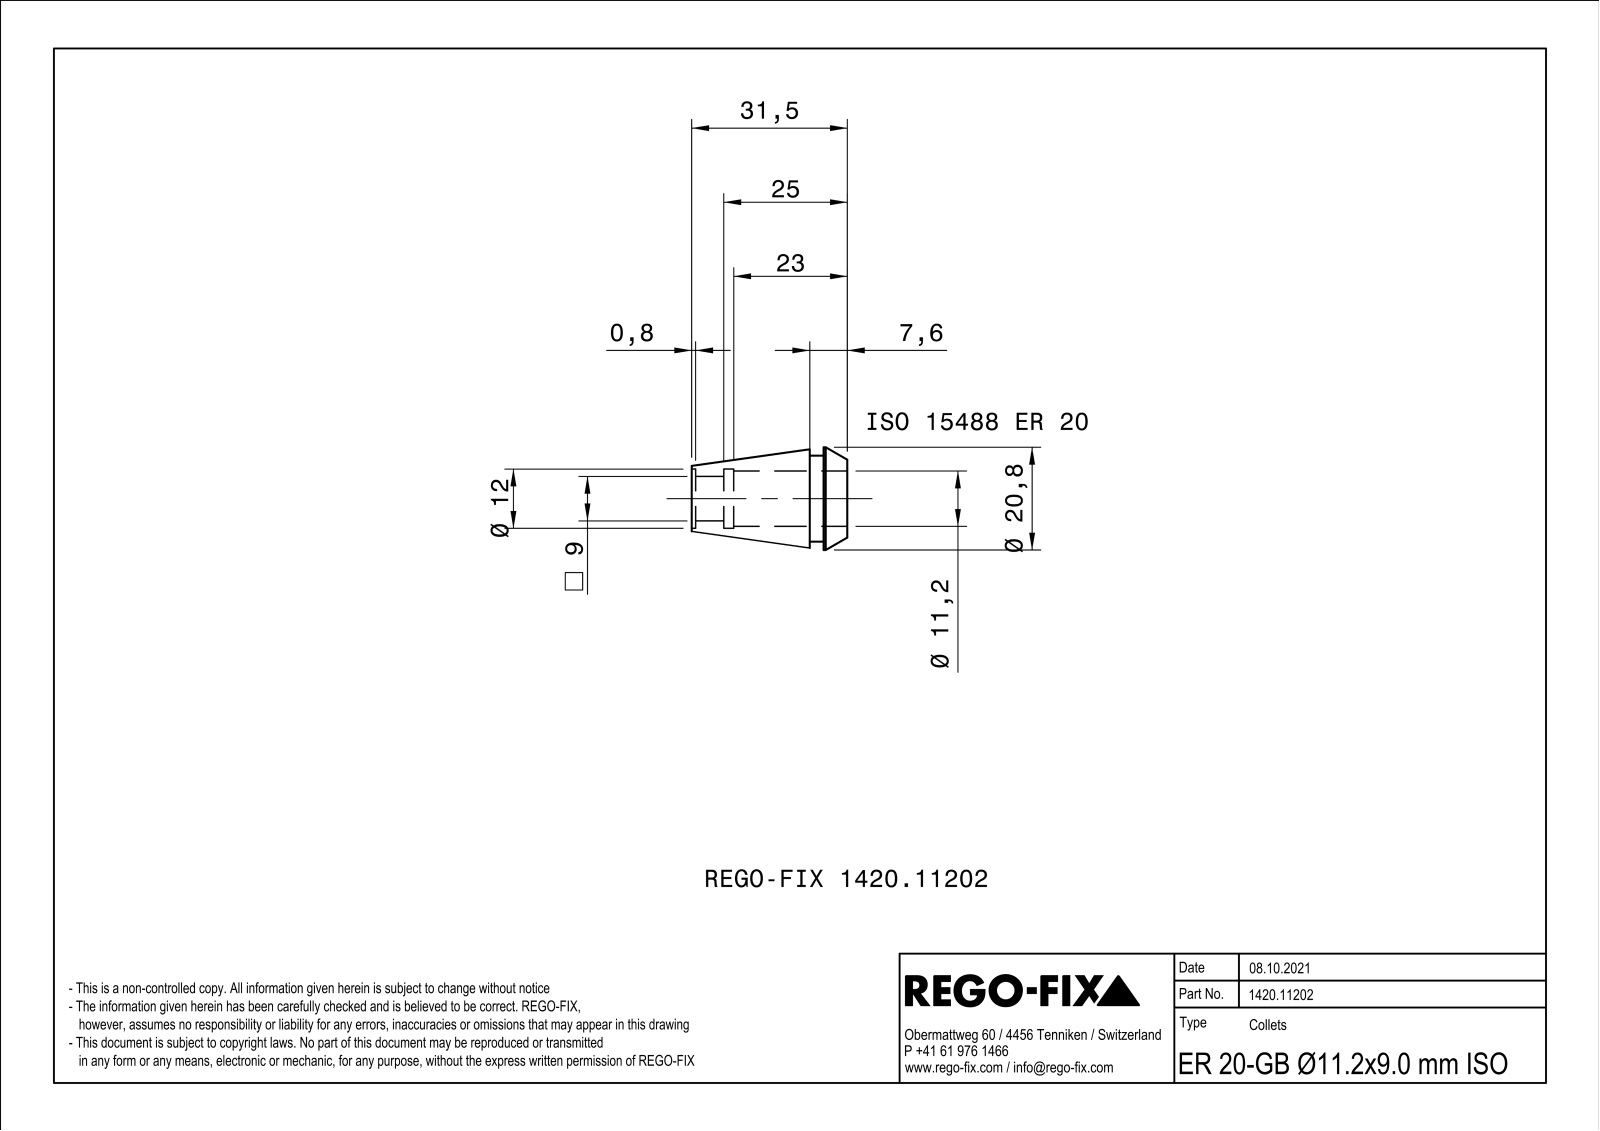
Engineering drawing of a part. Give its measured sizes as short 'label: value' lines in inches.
name: NOCUT
written by: SIEMENS PLM Software Solid Edge ST10 (AUTOMOTIVE_DESIGN)
unit: in
bodies: 1 solid, 144 faces (60 planar, 32 cylindrical, 52 other)
size: 1.24 × 0.819 × 0.819
volume: 0.219 in³; area: 6.279 in²
holes: 1× ⌀0.441, 1× ⌀0.472
bosses: 1× ⌀0.685
rounds: 1× R0.199, 1× R0.228
face distances: 0.031, 0.189, 0.171, 0.203, 0.299, 0.11, 0.374, 0.827, 0.638, 0.528
